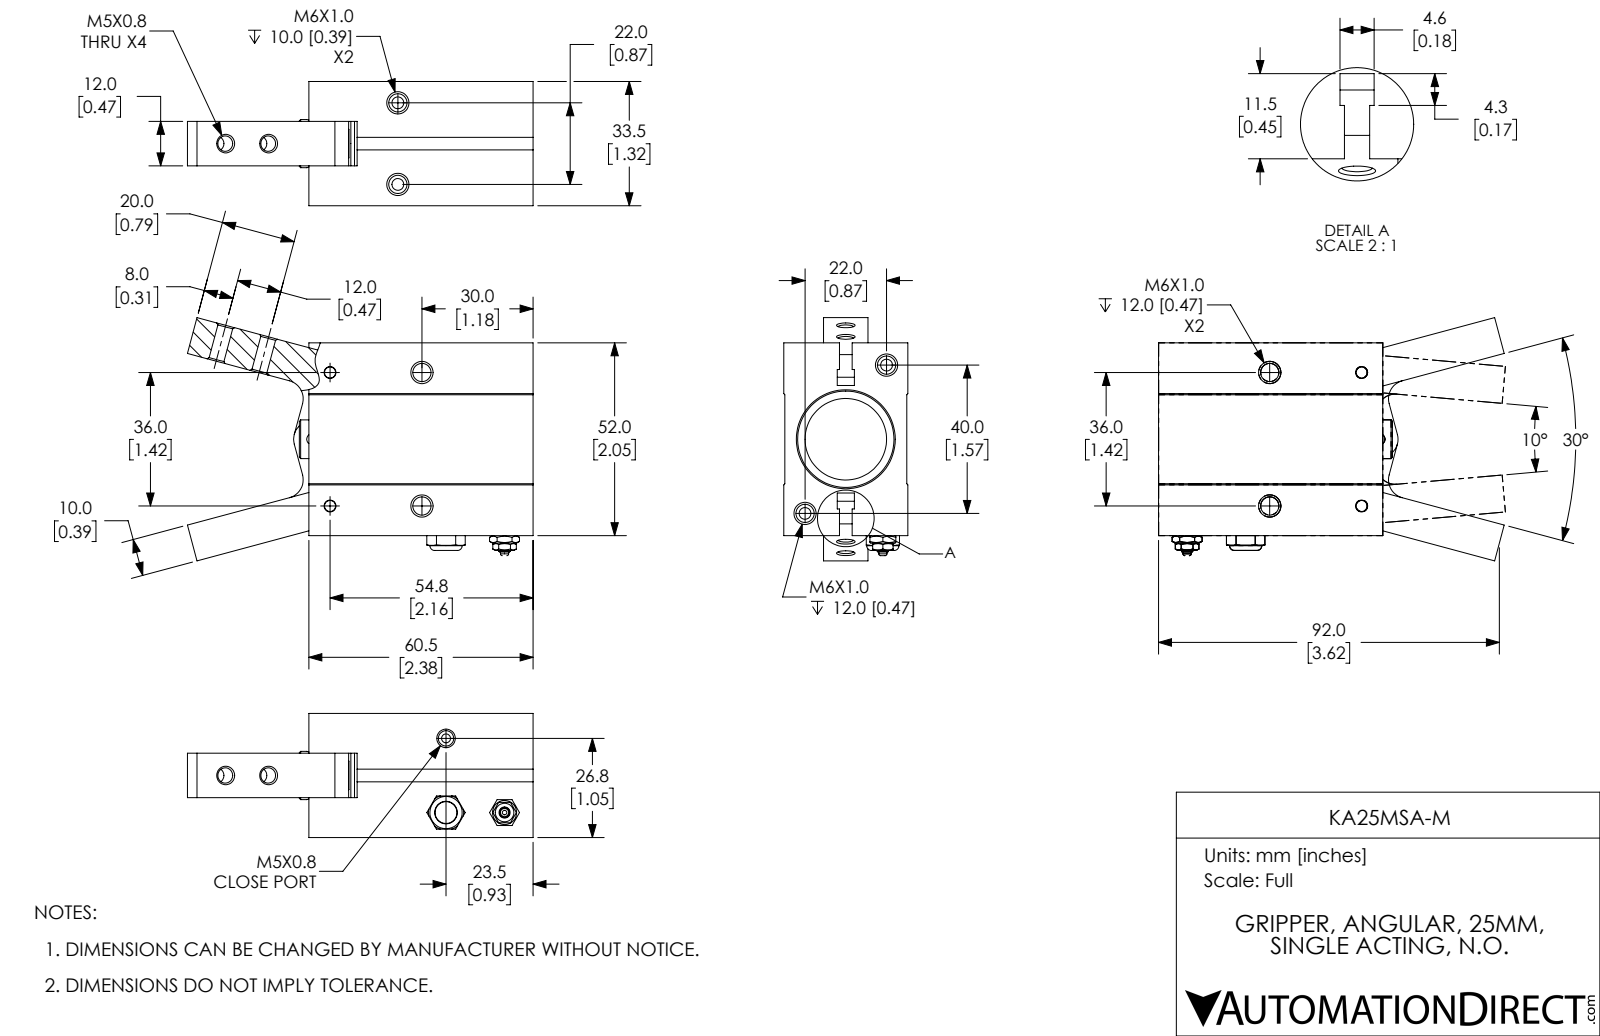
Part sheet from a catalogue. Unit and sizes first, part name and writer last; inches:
Units: inches
Overall size (bounding box): 3.672 × 2.582 × 1.319
Round holes (diameter × count): ⌀0.163 ×6, ⌀0.194 ×4, ⌀0.118 ×3, ⌀0.194 ×2, ⌀0.244 ×2, ⌀0.551 ×1, ⌀0.866 ×1, ⌀0.984 ×1, ⌀1.024 ×1, ⌀1.063 ×1
Round bosses / shafts (diameter × count): ⌀0.98 ×1, ⌀0.512 ×1, ⌀0.394 ×1, ⌀0.343 ×1, ⌀0.118 ×1, ⌀0.087 ×1
Partial cylindrical surfaces — rounded edges, fillets, slot ends (radius × count): R0.197 ×4
Main face-to-face distances: 1.307, 0.423, 0.896, 0.411, 0.884, 1.295, 1.319, 2.047, 0.303, 0.169
Hole centre spacings: 0.472, 0.513, 0.733, 0.899, 0.972, 0.976, 1.364, 1.417
Volume: 5.626 in³ · Surface area: 51.11 in²
Bodies: 4 solids, 294 faces (114 planar, 92 cylindrical, 88 other)
Part name (STEP PRODUCT): KA25MSA-M; KA25MSA-M-4; KA25MSA-M-1; KA25MSA-M-3 (+1 more)
STEP written by: SolidWorks 2017 (AUTOMOTIVE_DESIGN)
